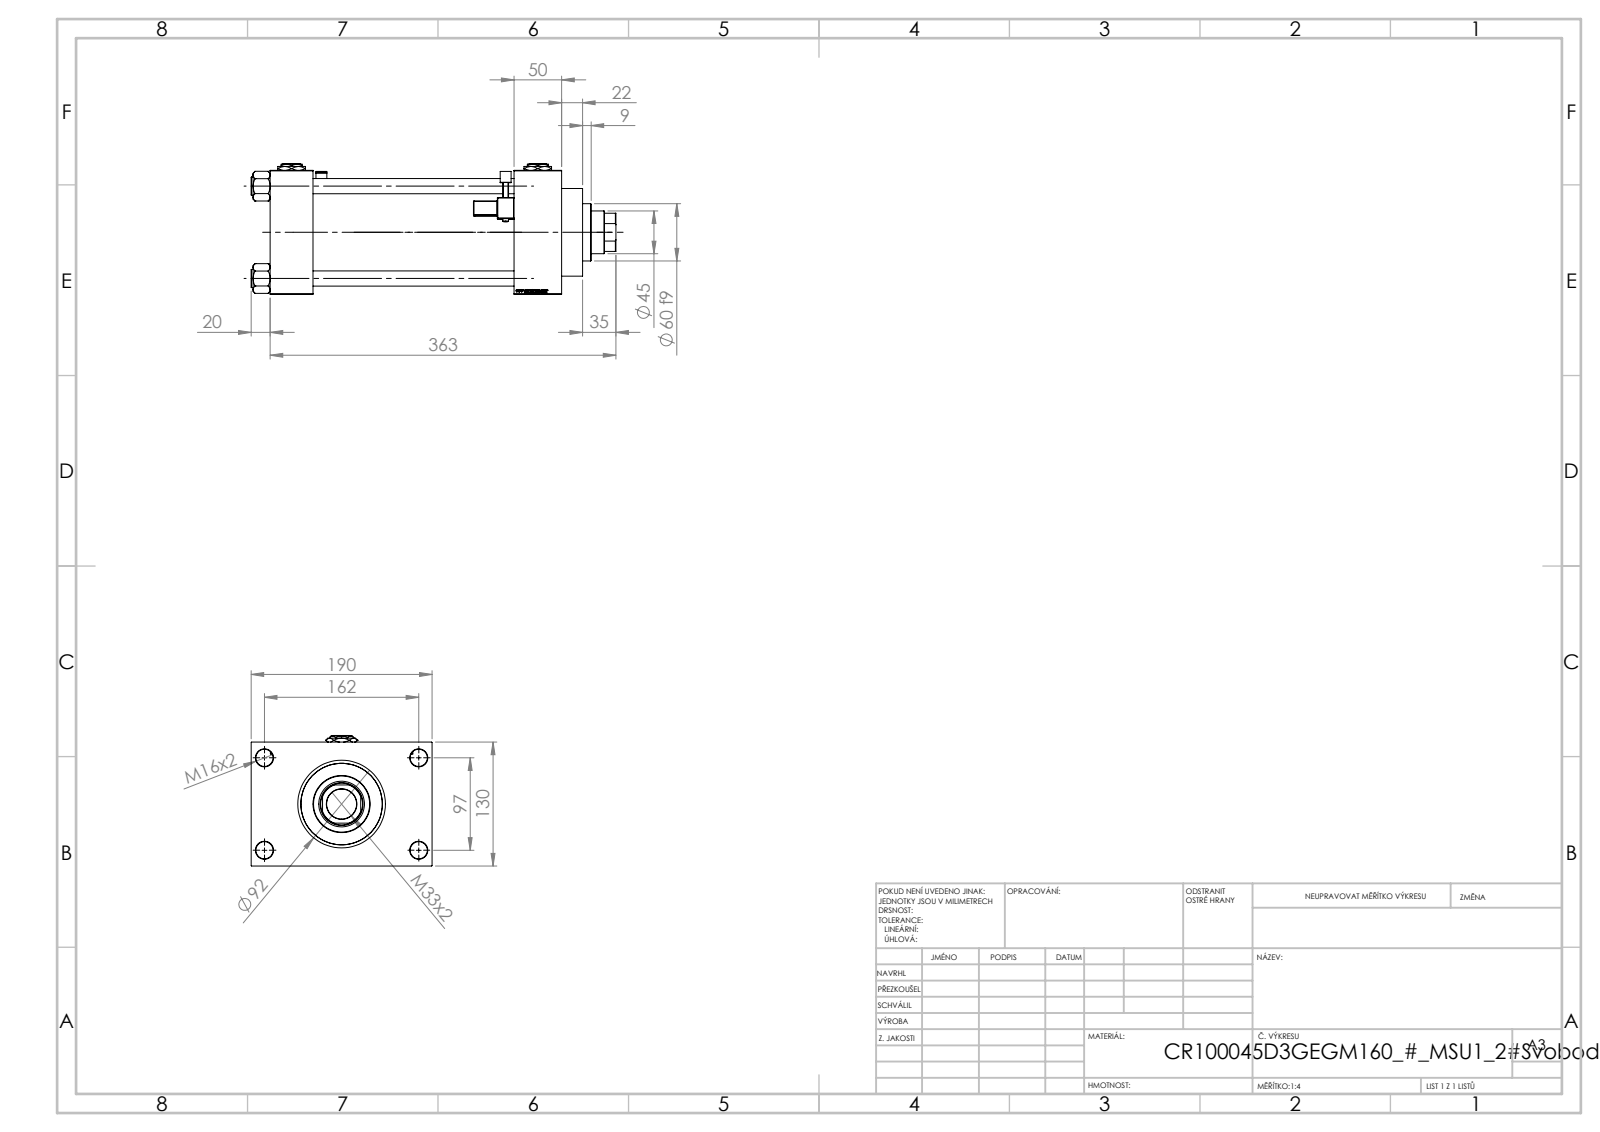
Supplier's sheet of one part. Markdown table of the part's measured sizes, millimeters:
| quantity | value |
| --- | --- |
| part name | V215CR_VCP_D; V215CR_D_Body; V215CR_MSU; V215_VC_A (+3 more) |
| STEP written by | SolidWorks 2019 (CONFIG_CONTROL_DESIGN) |
| units | millimeters |
| bodies | 15 solids, 1407 faces (651 planar, 160 cylindrical, 596 other) |
| overall size | 383 × 190 × 137 |
| volume | 3 105 000 mm³ |
| surface area | 510 308 mm² |
| round holes (diameter × count) | 16 × 4, 18 × 4, 7 × 2, 26.44 × 2, 35 × 2, 31.5 × 1, 45 × 1, 48 × 1, 76 × 1, 85.5 × 1, 100 × 1 |
| round bosses / shafts (diameter × count) | 19 × 4, 6 × 2, 106 × 1, 92 × 1, 60 × 1 |
| partial cylindrical surfaces (radius × count) | 0.5 × 48, 1 × 2, 2.5 × 2, 4 × 2, 22 × 1 |
| main face-to-face distances | 130, 45, 160, 211, 256, 306, 261, 50, 30, 190 |
| hole center spacings | 32.55, 68.52, 94.41, 96.9, 102.27, 129.45, 161.73, 97 |
